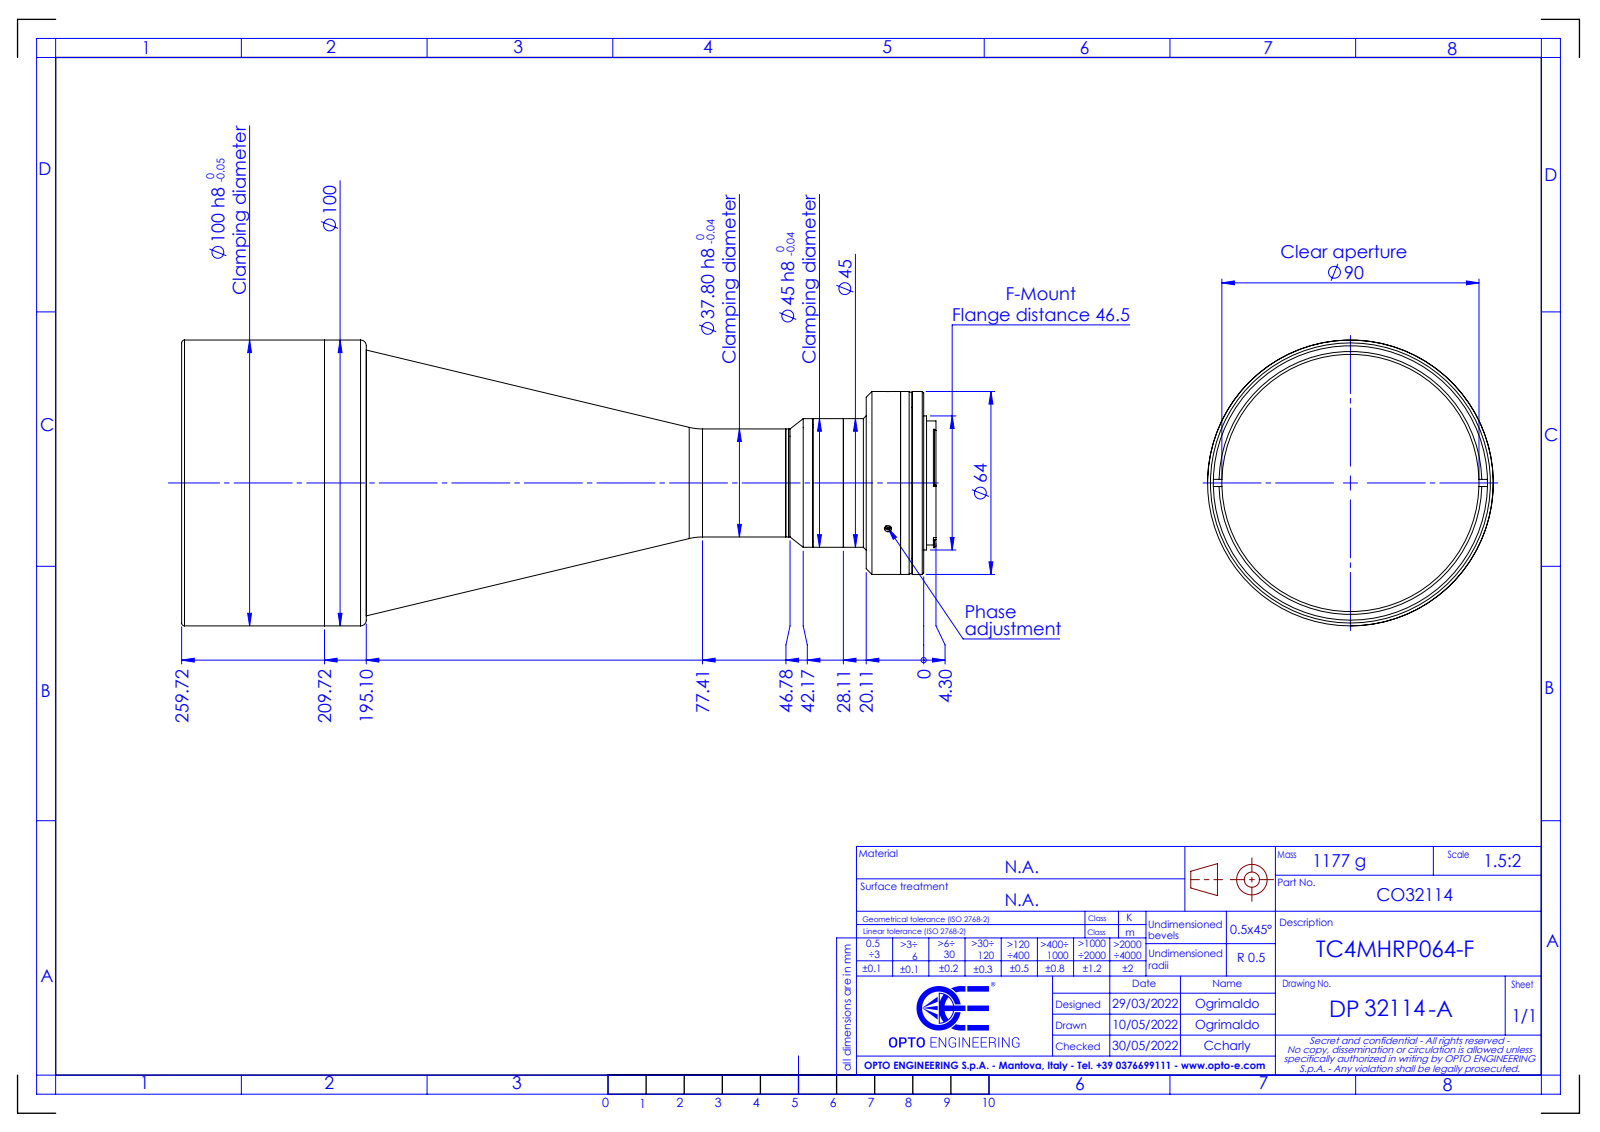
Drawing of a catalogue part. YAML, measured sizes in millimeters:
part_name: "DP32114-A_TC4MHRP064-F"
step_written_by: "SolidWorks 2021 (CONFIG_CONTROL_DESIGN)"
units: millimeters
bodies: {solids: 0, faces: 132, planar: 42, cylindrical: 56, other: 34}
overall_size: [264.02, 100, 100]
round_holes:
  - {diameter: 2.5, count: 3}
  - {diameter: 29, count: 1}
  - {diameter: 32, count: 1}
  - {diameter: 42, count: 1}
  - {diameter: 90, count: 1}
  - {diameter: 93, count: 1}
  - {diameter: 96, count: 1}
round_bosses_or_shafts:
  - {diameter: 100, count: 1}
  - {diameter: 64, count: 1}
  - {diameter: 63.5, count: 1}
  - {diameter: 46.9, count: 1}
  - {diameter: 45, count: 1}
  - {diameter: 43.4, count: 1}
  - {diameter: 37.8, count: 1}
partial_cylinders:
  - {radius: 0.5, count: 2}
  - {radius: 1.15, count: 2}
  - {radius: 22.65, count: 1}
face_to_face_distances: [3, 8.09, 5.09, 12.02, 15.02, 20.11, 16.11, 4.09, 1.09, 4]
